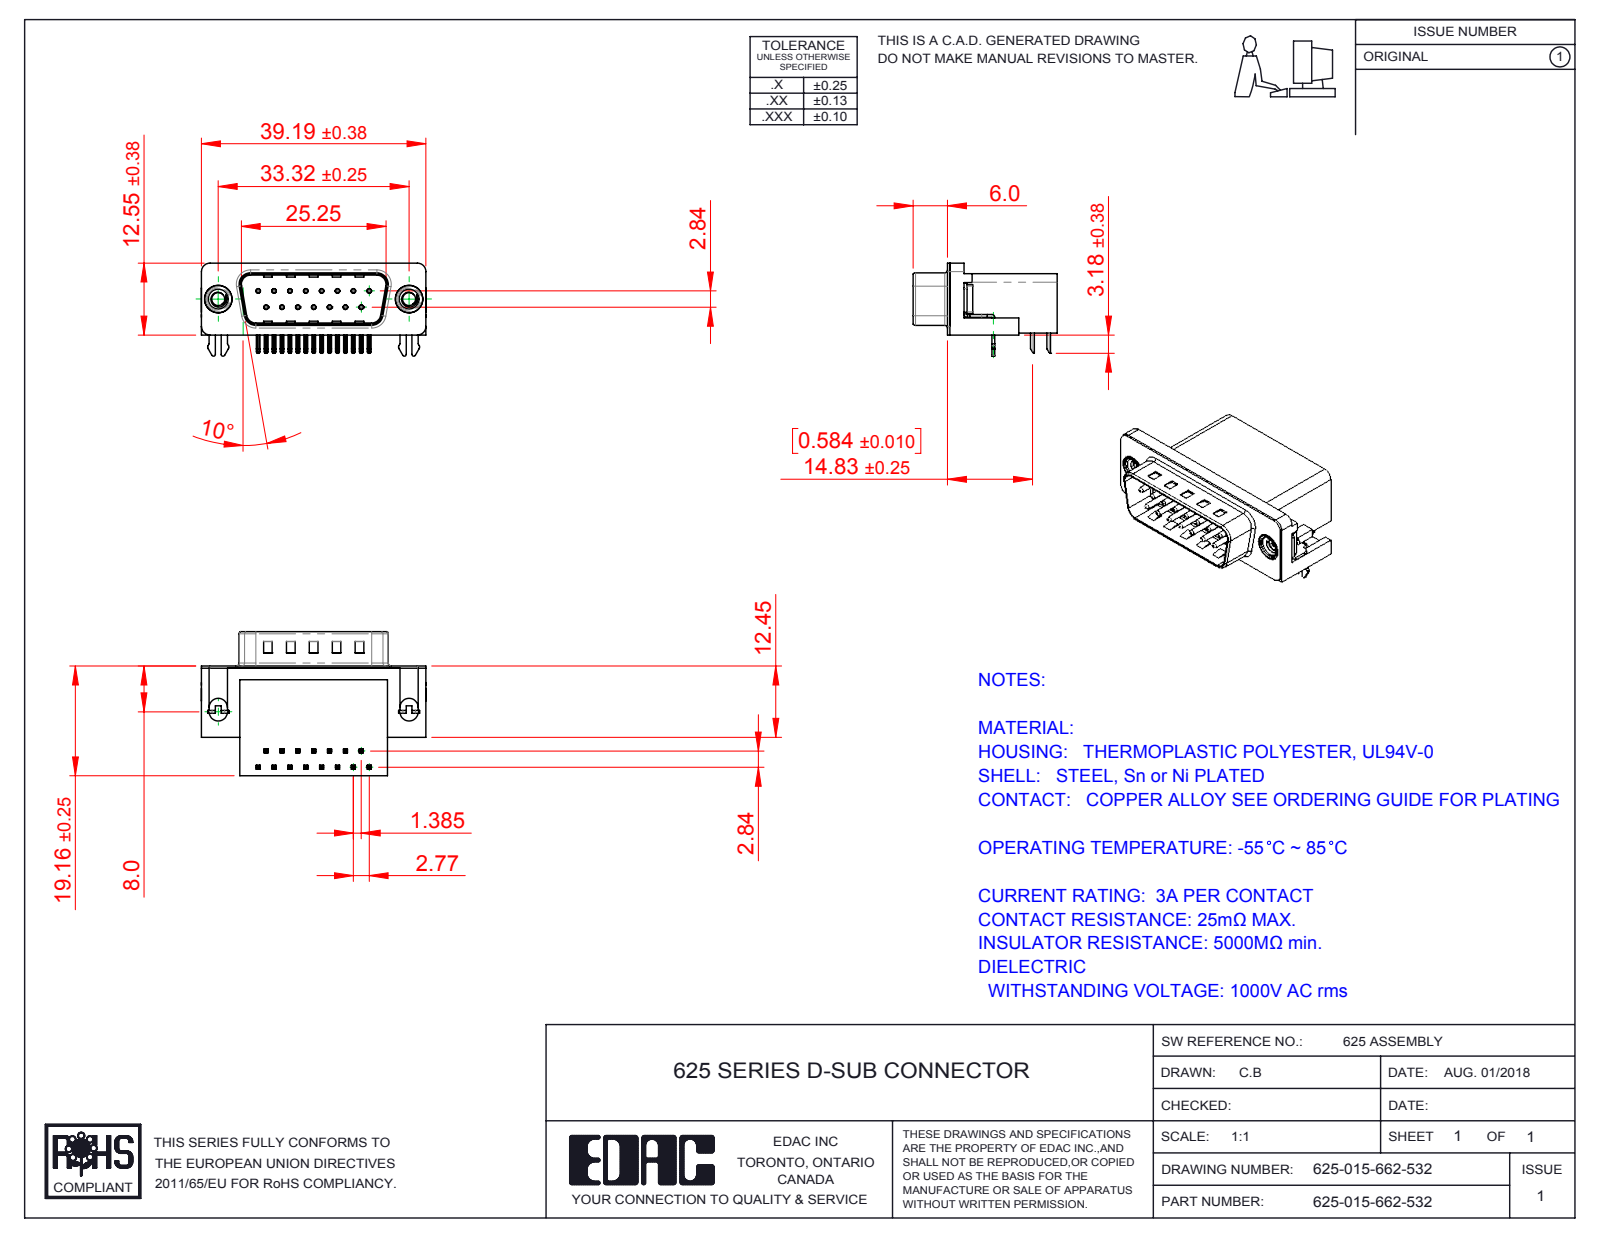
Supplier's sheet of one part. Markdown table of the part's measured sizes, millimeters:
| quantity | value |
| --- | --- |
| part name | 625 Contact Top; 625 Contact Bottom; 625 2 Prong Board Lock; 625-015-662-532 (+3 more) |
| STEP written by | SolidWorks 2016 (CONFIG_CONTROL_DESIGN) |
| units | millimeters |
| bodies | 21 solids, 1519 faces (925 planar, 455 cylindrical, 139 other) |
| overall size | 39.22 × 25.16 × 16.25 |
| volume | 6 243 mm³ |
| surface area | 6 431 mm² |
| round holes (diameter × count) | 0.35 × 15, 0.8 × 15, 2.26 × 2, 4 × 2, 4.8 × 2, 5 × 2 |
| round bosses / shafts (diameter × count) | 0.75 × 15, 4.9 × 2, 4.75 × 2, 3.9 × 2 |
| partial cylindrical surfaces (radius × count) | 0.25 × 68, 0.12 × 30, 1 × 16, 0.5 × 14, 1.6 × 8, 1.5 × 6, 0.32 × 4, 0.9 × 4 |
| main face-to-face distances | 0.4, 10.35, 18.76, 2.1, 10.46, 19.16, 1.7, 10.86, 8.76, 16.26 |
| hole center spacings | 3.16, 2.77, 5.54, 8.31, 11.08, 5.03, 5.04, 7.48 |
